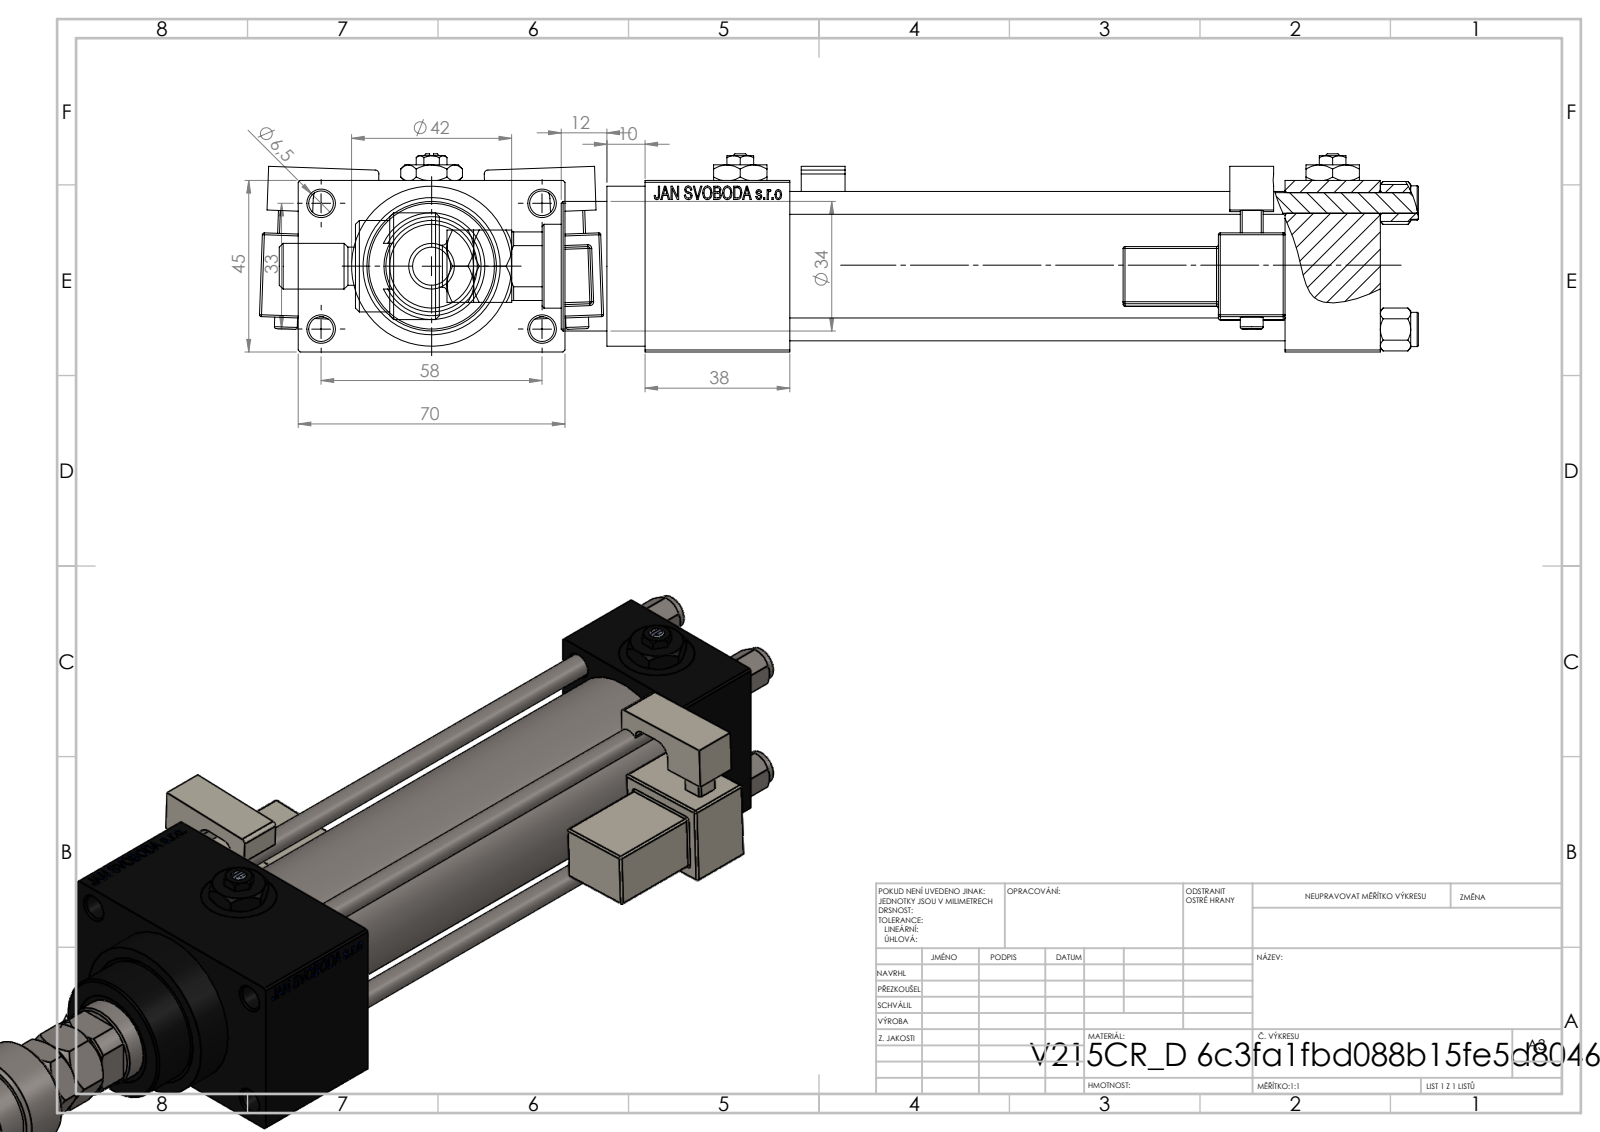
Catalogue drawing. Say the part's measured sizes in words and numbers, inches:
The part is named "V215_VC_A; MFA; V215CR_D_TYCINKA; V215CR_D_Body (+5 more)". Its 3-D file was written by "SolidWorks 2019 (CONFIG_CONTROL_DESIGN)". It is 17 solids with 1446 faces: 632 planar, 172 cylindrical and 642 other. Overall it measures 11.772 by 3.556 by 2.047 inches. Its volume is 22.34 cubic inches and its surface area 201.3 square inches. Round holes: 4 of diameter 0.236, 4 of diameter 0.256, 4 of diameter 0.518, 4 of diameter 0.787, 3 of diameter 0.276, 1 of diameter 0.413, 1 of diameter 0.866, 1 of diameter 0.945, 1 of diameter 0.984, 1 of diameter 1.26, 1 of diameter 1.299. Round bosses or shafts: 4 of diameter 0.354, 2 of diameter 0.236, 1 of diameter 1.654, 1 of diameter 1.496, 1 of diameter 1.339, 1 of diameter 1.102, 1 of diameter 0.709, 1 of diameter 0.472. Partial cylindrical surfaces (rounded edges, fillets, slot ends): 48 of radius 0.02, 2 of radius 0.039, 2 of radius 0.098, 2 of radius 0.157, 1 of radius 0.384, 1 of radius 0.413. The main face-to-face distances are 1.772, 0.984, 5.118, 0.492, 2.264, 0.118, 6.102, 6.614, 1.496, 7.598. The hole center spacings are 0.488, 0.924, 1.307, 1.314, 1.392, 1.795, 2.219, 1.299.
